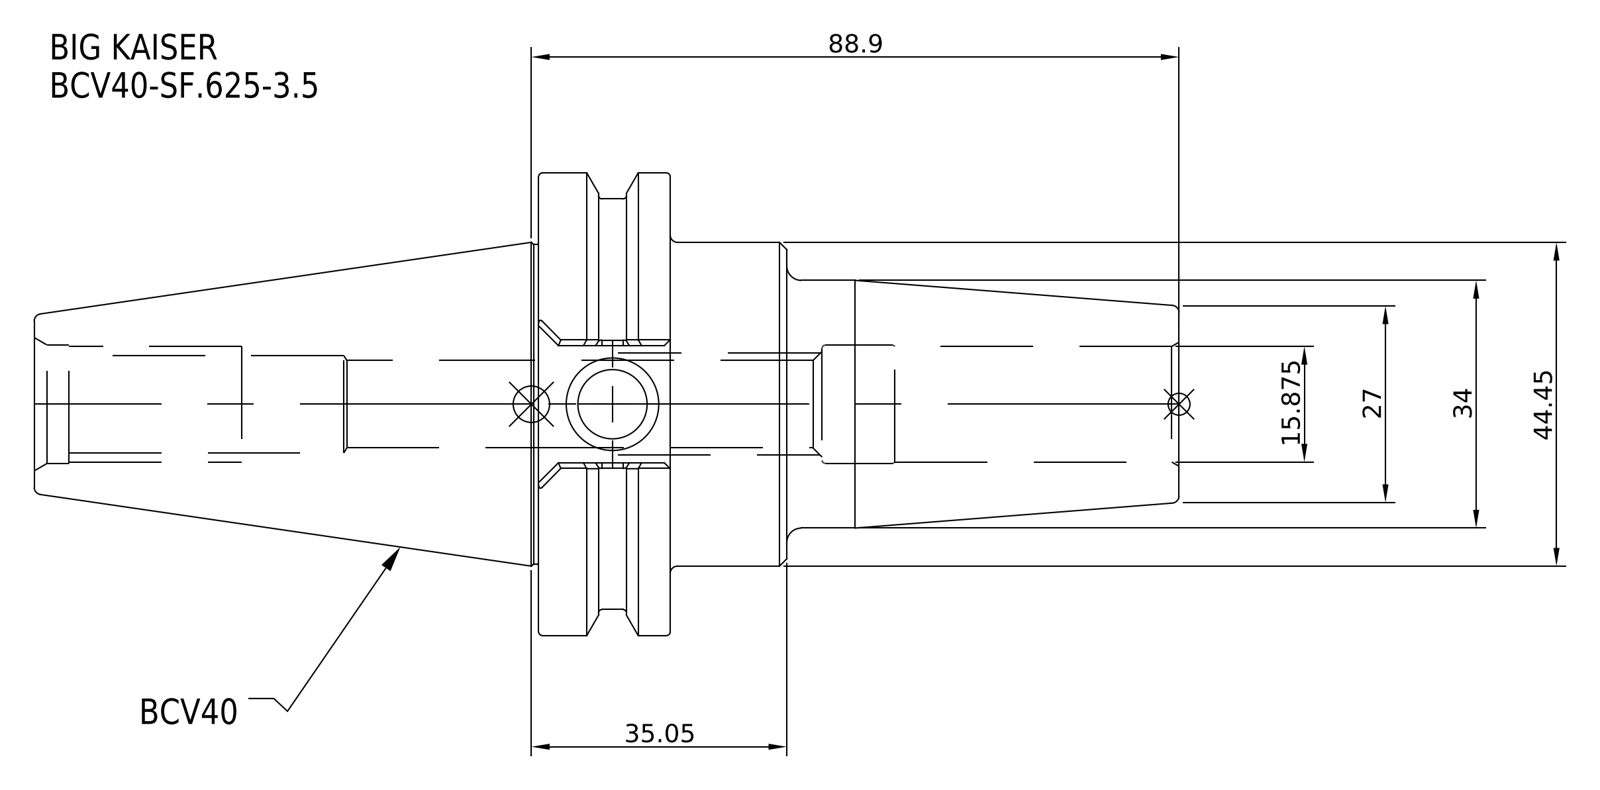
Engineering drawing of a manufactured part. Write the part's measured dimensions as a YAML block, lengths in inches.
part_name: "BCV40-SF_625-3_5"
step_written_by: "SolidWorks 2021 (CONFIG_CONTROL_DESIGN)"
units: inches
bodies: {solids: 1, faces: 30, planar: 8, cylindrical: 14, other: 8}
overall_size: [6.187, 2.5, 2.5]
volume: 10.93
surface_area: 40.88
round_holes:
  - {diameter: 0.625, count: 1}
round_bosses_or_shafts:
  - {diameter: 2.5, count: 1}
  - {diameter: 2.219, count: 1}
  - {diameter: 1.75, count: 1}
  - {diameter: 1.339, count: 1}
face_to_face_distances: [0.711, 0.63, 1.341, 4.067, 3.437, 2.726, 2.12, 2.75, 3.461, 6.187]
